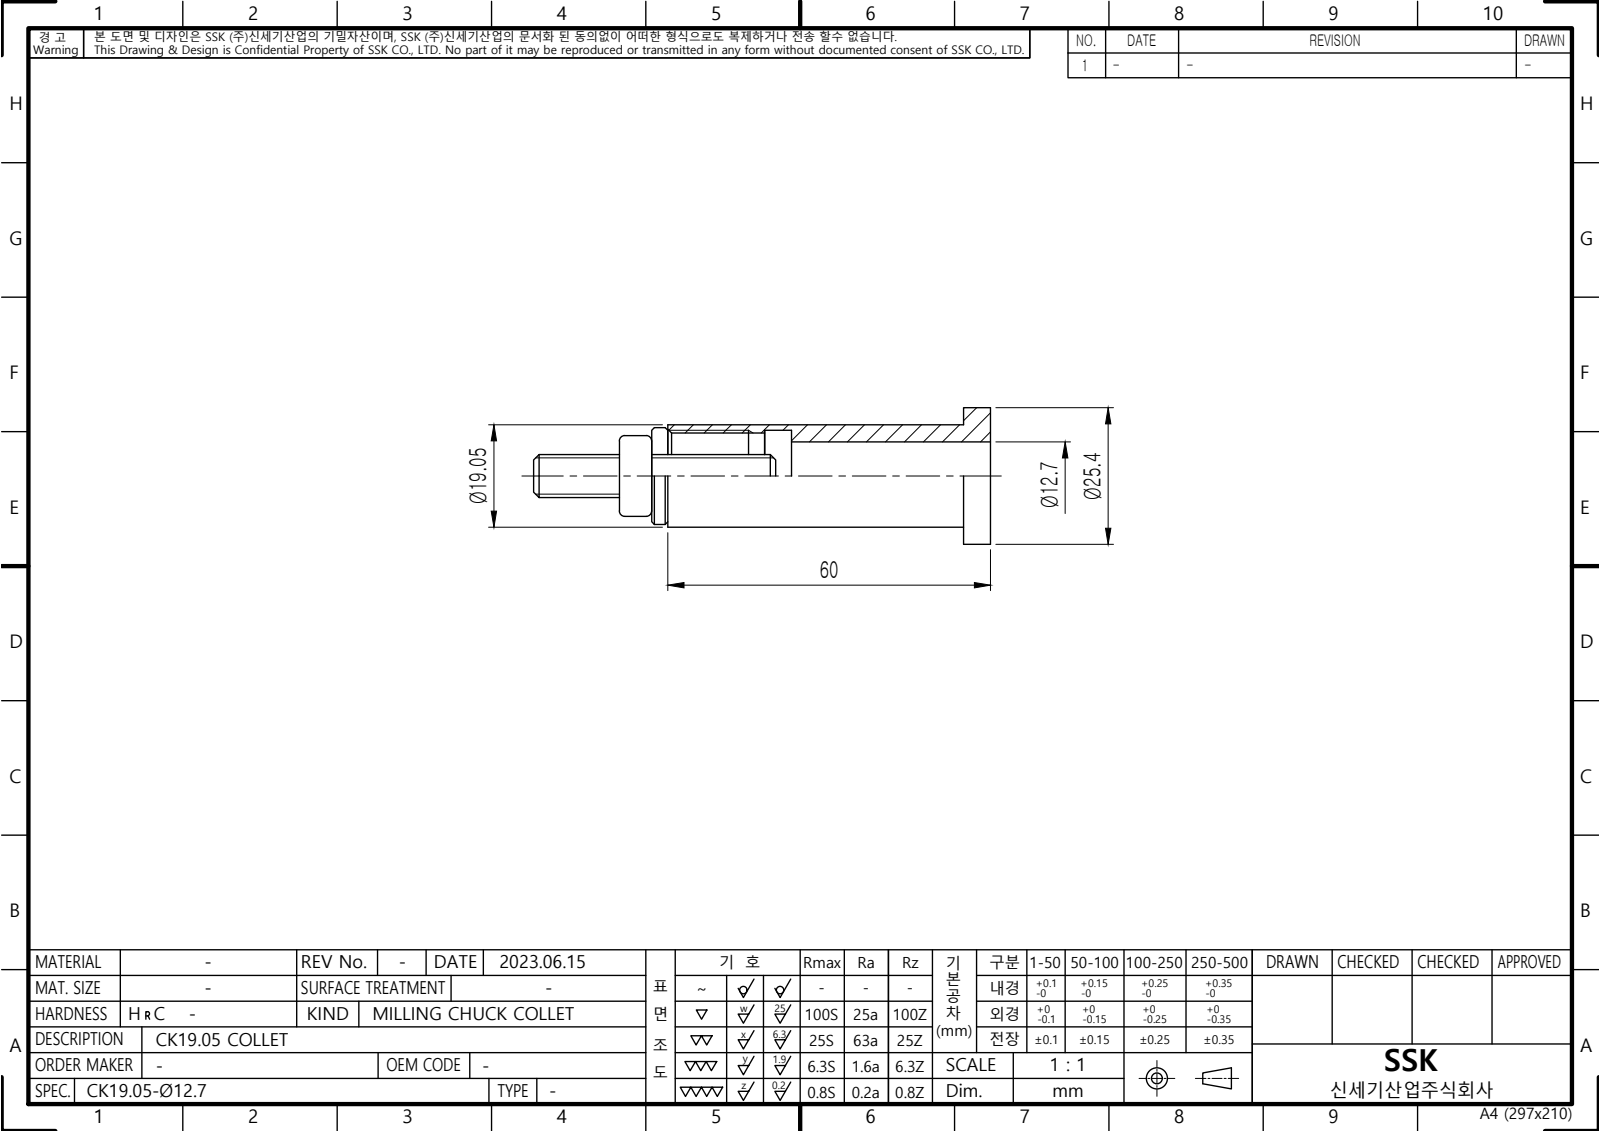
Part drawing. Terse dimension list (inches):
name: LO-CK19.05-12.7
written by: Autodesk Inventor 2022 (AUTOMOTIVE_DESIGN)
unit: in
bodies: 1 solid, 10 faces (5 planar, 5 cylindrical, 0 other)
size: 2.362 × 1 × 1
volume: 0.537 in³; area: 11.08 in²
holes: 1× ⌀0.5, 1× ⌀0.627, 1× ⌀0.669
bosses: 1× ⌀1, 1× ⌀0.75
face distances: 0.197, 1.457, 1.26, 0.906, 2.165, 2.362, 0.709, 1.654
